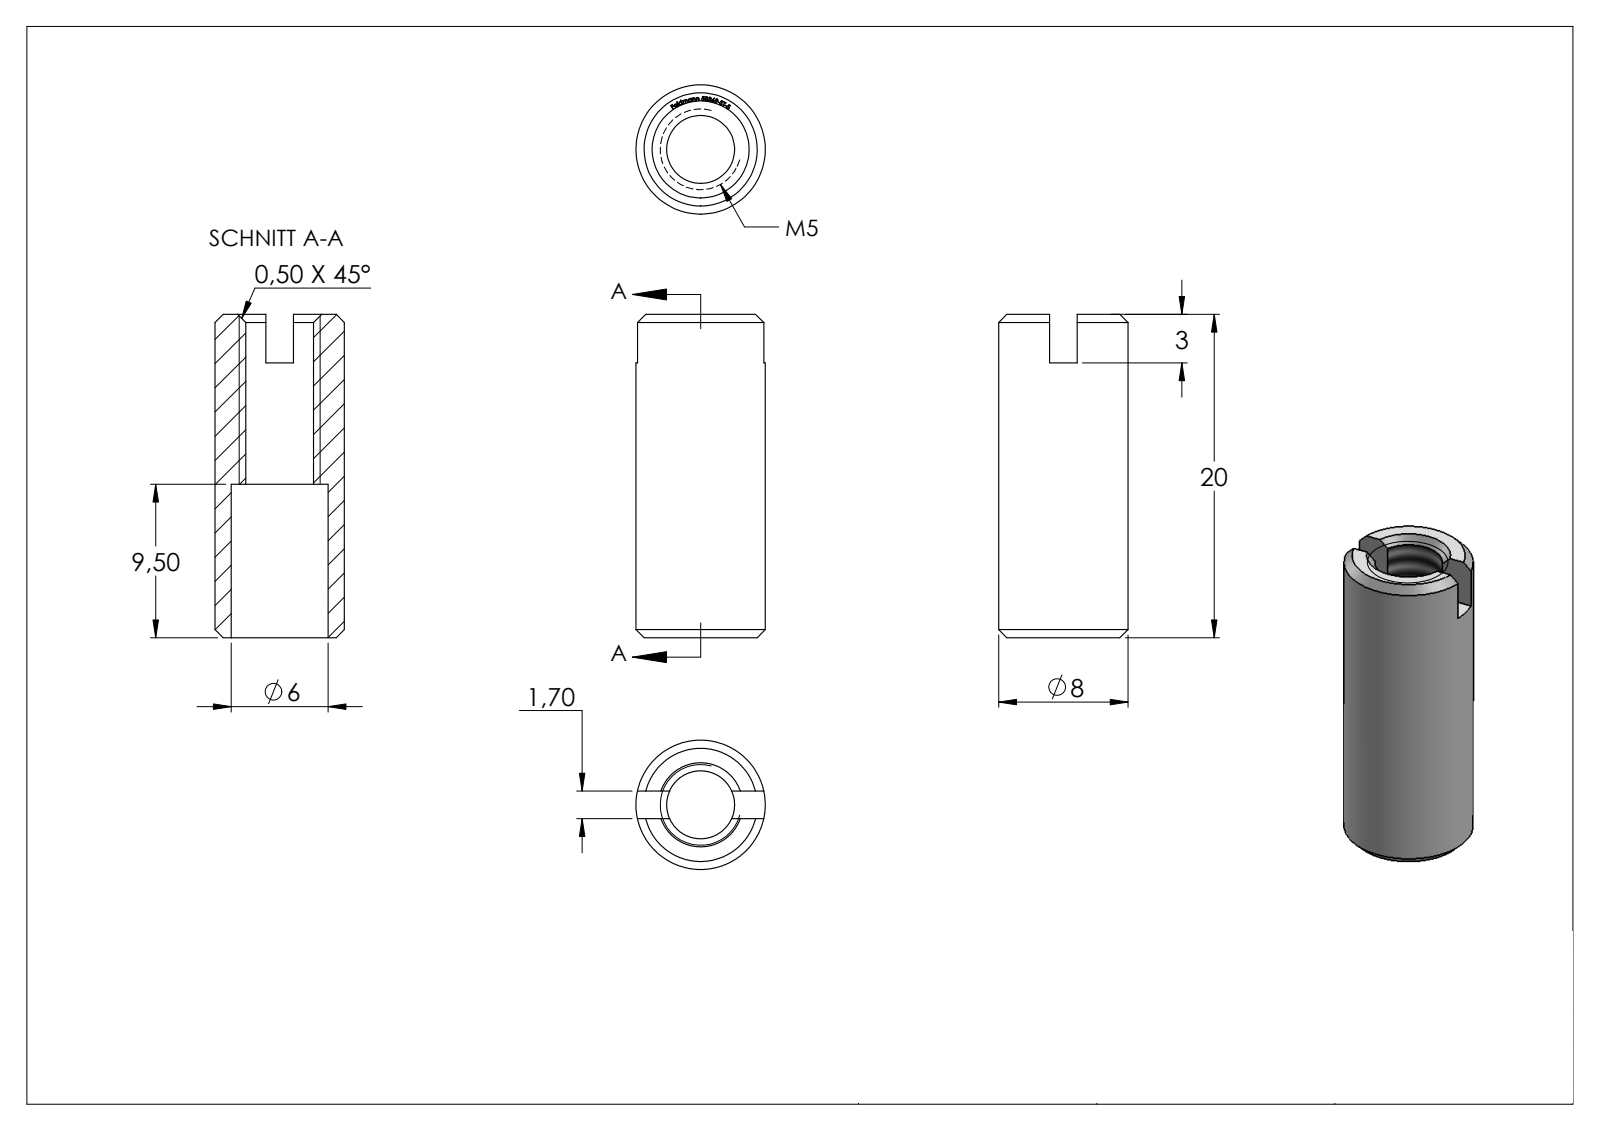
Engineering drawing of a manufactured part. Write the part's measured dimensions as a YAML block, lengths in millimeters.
part_name: "58369-ST-5"
step_written_by: "SolidWorks 2015 (CONFIG_CONTROL_DESIGN)"
units: millimeters
bodies: {solids: 1, faces: 299, planar: 140, cylindrical: 7, other: 152}
overall_size: [26, 8, 8]
volume: 565
surface_area: 880
round_holes:
  - {diameter: 4.2, count: 1}
  - {diameter: 6, count: 1}
round_bosses_or_shafts:
  - {diameter: 8, count: 1}
face_to_face_distances: [10.5, 1.7, 9.5, 20, 17, 7.5, 3, 9.4, 16.9, 19.9]
